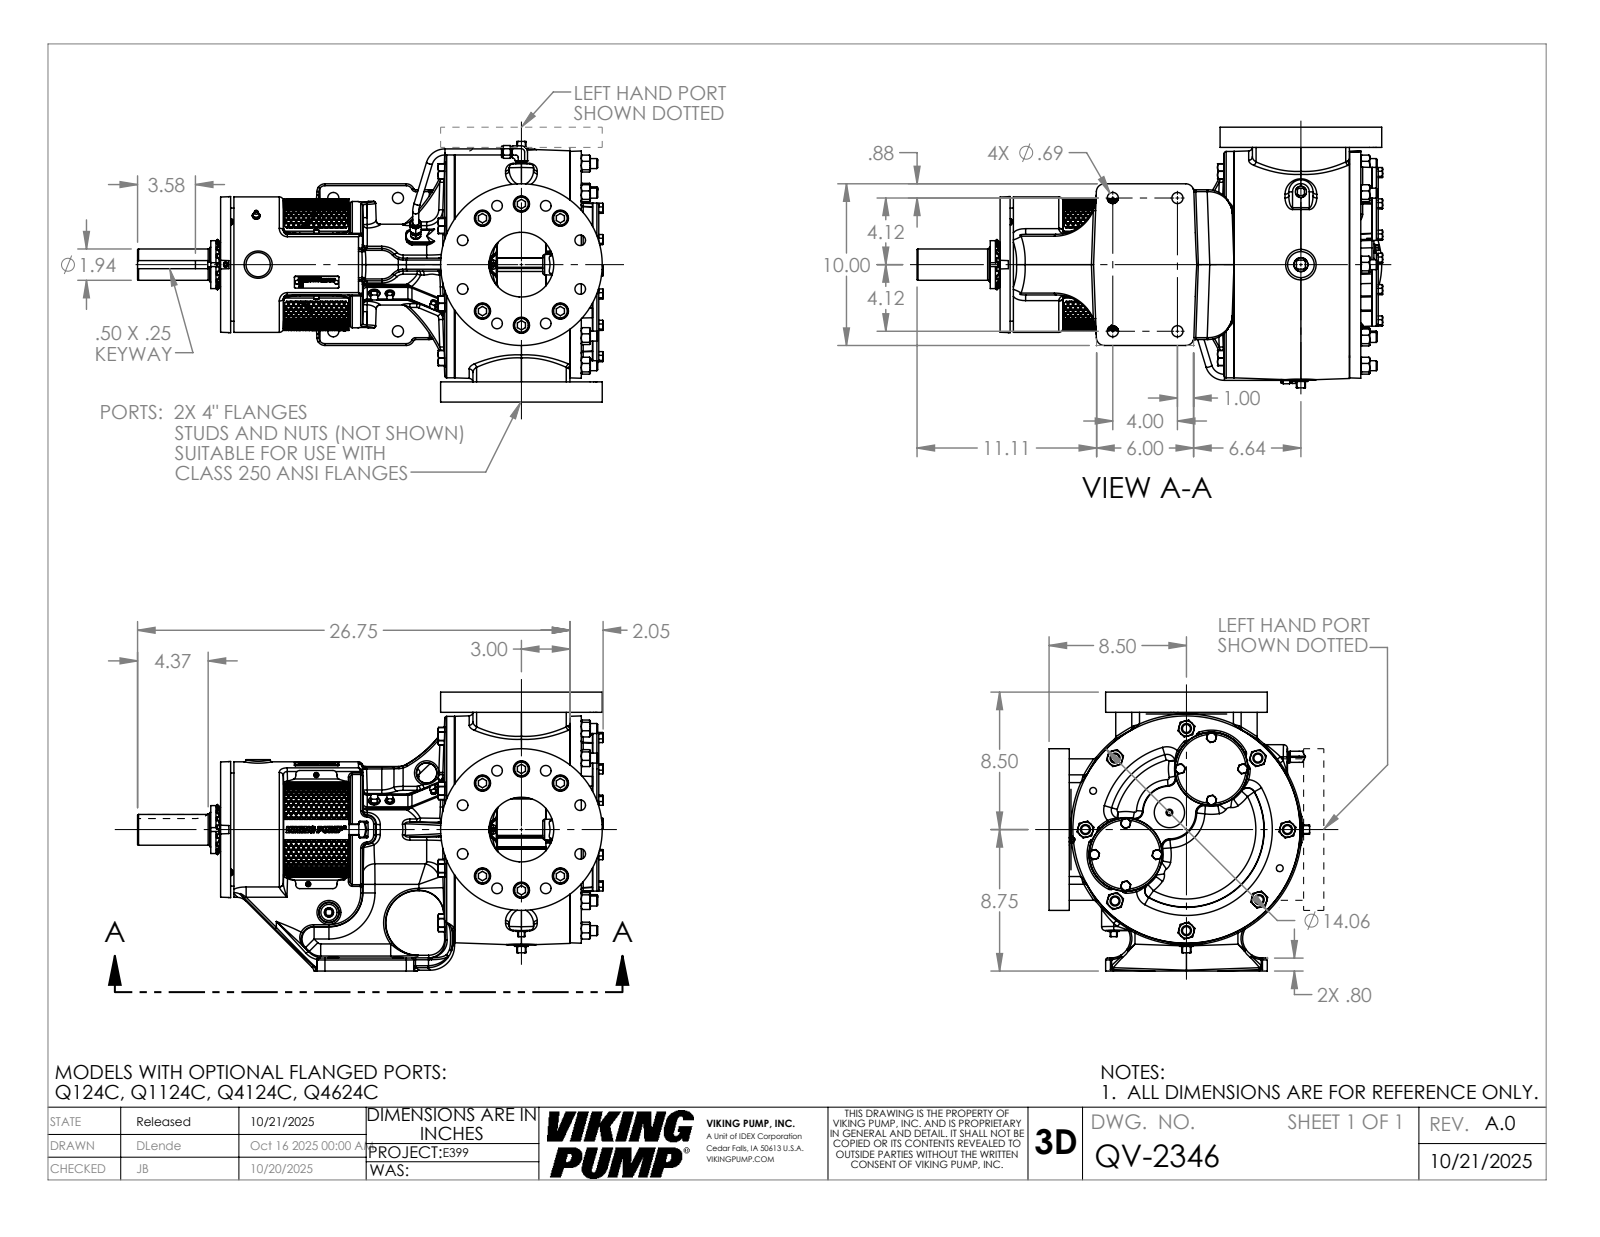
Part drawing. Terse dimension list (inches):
name: QV-2346
written by: SolidWorks 2024 (AUTOMOTIVE_DESIGN)
unit: in
bodies: 1 solid, 4098 faces (1428 planar, 676 cylindrical, 1994 other)
size: 28.804 × 17.25 × 16.221
volume: 2 111 in³; area: 2 205 in²
holes: 16× ⌀0.656, 12× ⌀1, 9× ⌀0.25, 8× ⌀0.266, 8× ⌀1.157, 4× ⌀0.688, 2× ⌀0.159, 2× ⌀0.313, 2× ⌀0.422, 2× ⌀4, 1× ⌀0.453, 1× ⌀2.157
bosses: 12× ⌀0.937, 8× ⌀0.617, 3× ⌀0.375, 3× ⌀0.312, 3× ⌀0.19, 2× ⌀10, 2× ⌀4.5, 2× ⌀0.687
rounds: 60× R0.12, 22× R0.25, 18× R0.015, 18× R0.092, 16× R0.07, 16× R0.75, 13× R0.5, 10× R0.24
face distances: 1.25, 17.25, 22.317, 16, 3.82, 18.498, 23.398, 19.578, 1.081, 7.972
hole spacings: 3.75, 7.276, 2.079, 3.937, 5.783, 1.184, 2.713, 3.013
